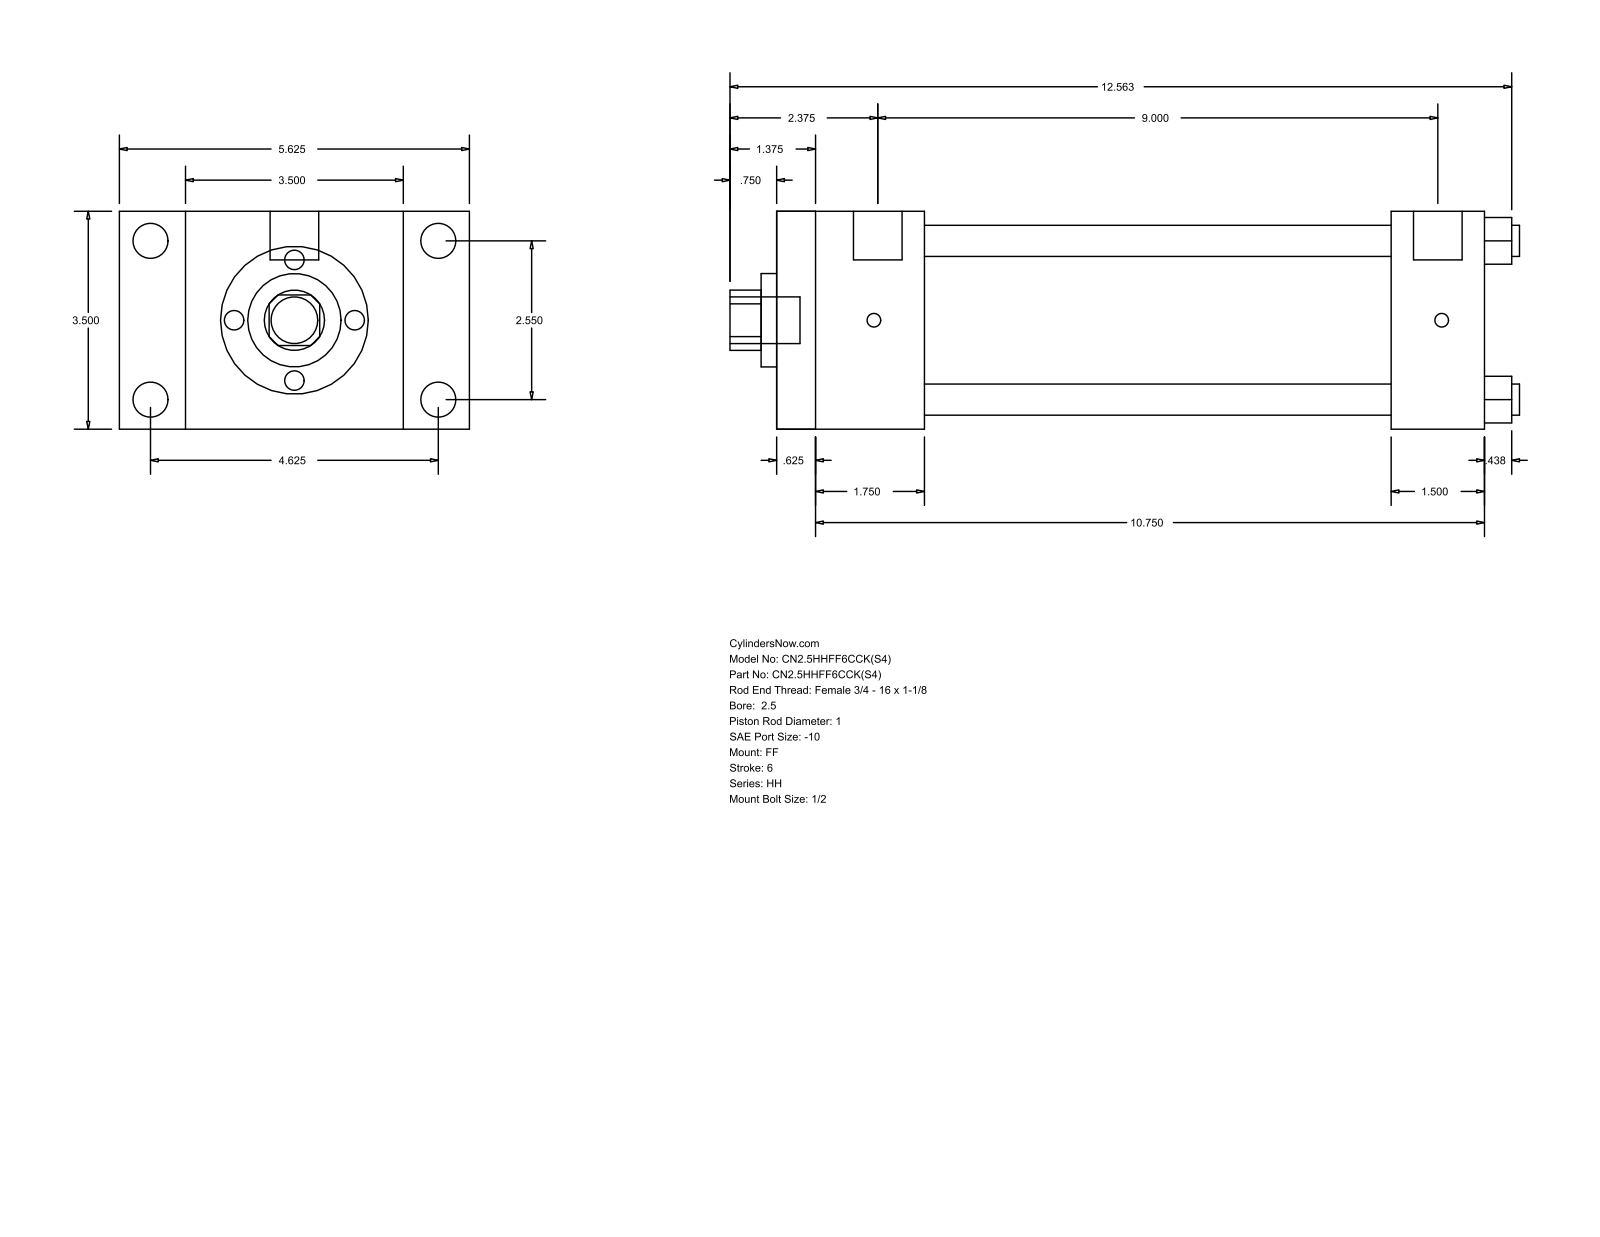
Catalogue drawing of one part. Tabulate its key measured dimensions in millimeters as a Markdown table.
| quantity | value |
| --- | --- |
| part name | HH_FF__0250_1 |
| STEP written by | GSSL Pune (CONFIG_CONTROL_DESIGN) |
| units | millimeters |
| bodies | 0 solids, 92 faces (64 planar, 28 cylindrical, 0 other) |
| overall size | 322.26 × 142.88 × 88.9 |
| round holes (diameter × count) | 12.7 × 4, 25.4 × 1, 38.1 × 1, 73.03 × 1 |
| round bosses / shafts (diameter × count) | 14.3 × 4, 5.56 × 4, 19.84 × 2, 19.05 × 1 |
| partial cylindrical surfaces (radius × count) | 12.29 × 1 |
| main face-to-face distances | 88.9, 288.93, 15.87, 273.06, 60.33, 44.46, 228.6, 250.83, 234.96, 190.5 |
| hole center spacings | 45.79, 64.76, 91.58 |
